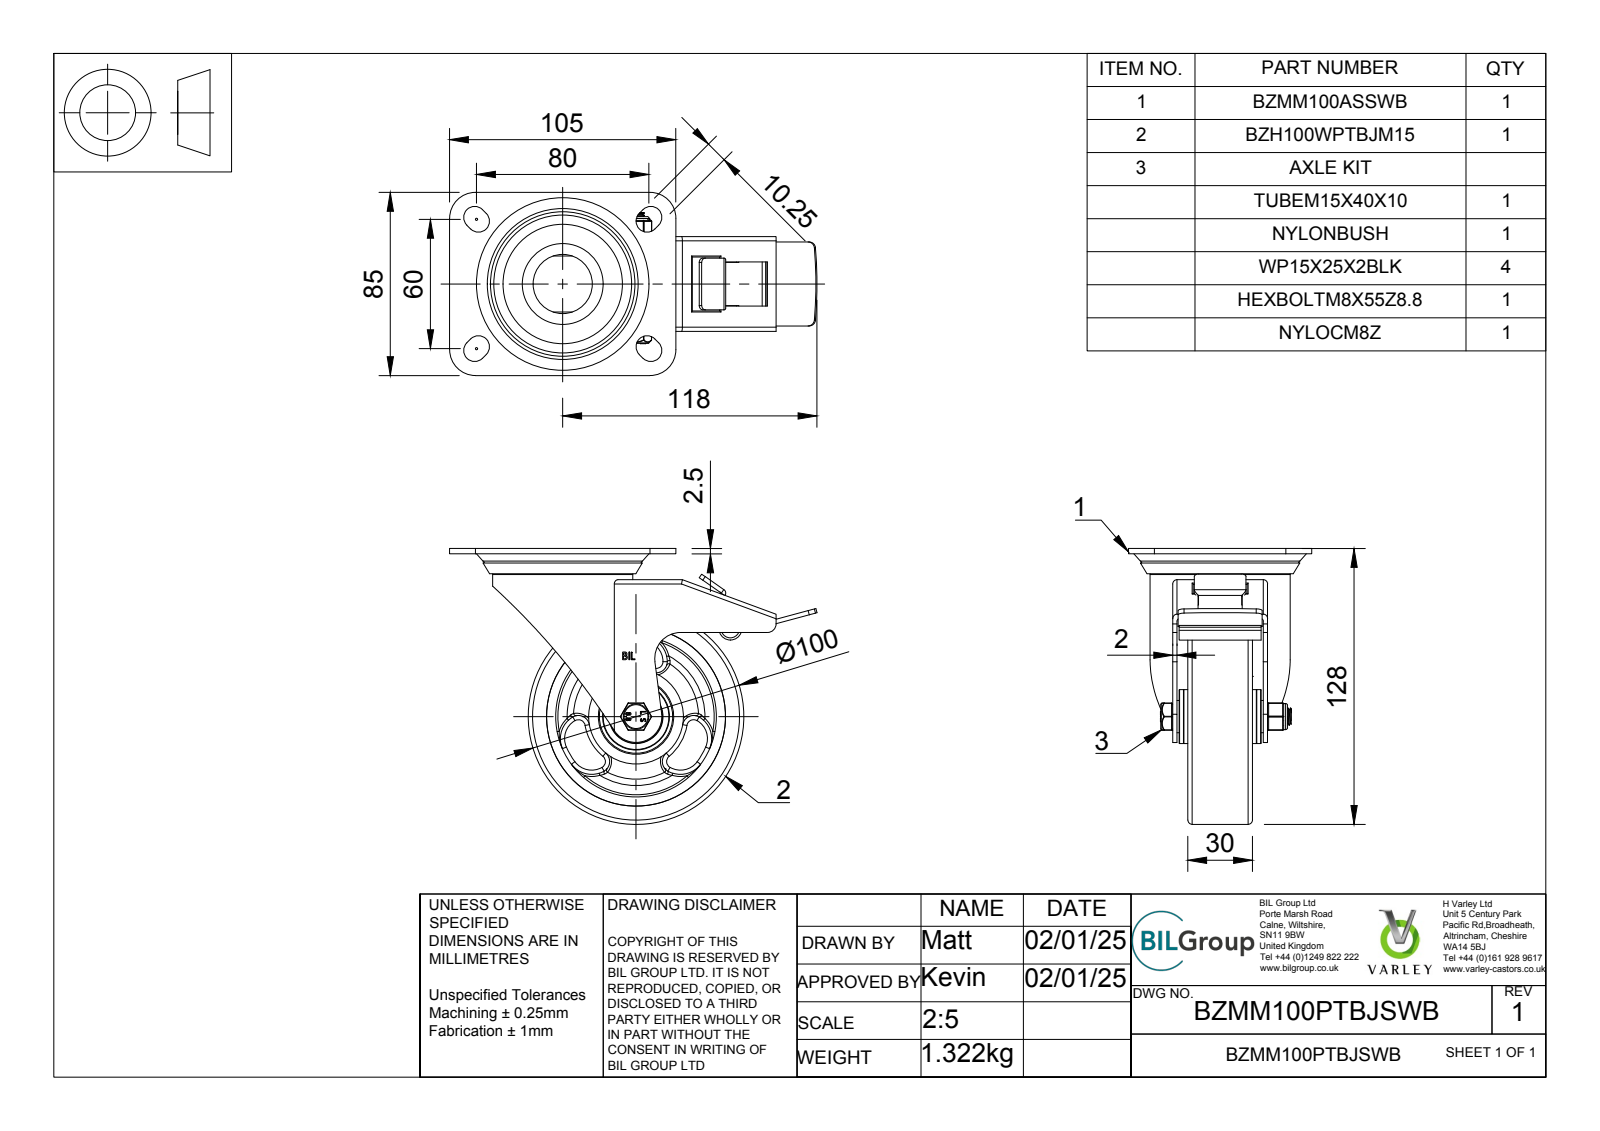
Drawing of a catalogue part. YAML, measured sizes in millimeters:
part_name: "BZMM100PTBJSWB v5; BZMM100ASSWB v1; ZINC PLATED, PRESSED STEEL TOP PLATE; ZINC PLATED, PRESSED STEEL TOP PLATE Geometry (+7 more)"
step_written_by: "Autodesk Translation Framework v13.20.0.188 (AP242_MANAGED_MODEL_BASED_3D_ENGINEERING_MIM_LF)"
units: millimeters
bodies: {solids: 67, faces: 1418, planar: 569, cylindrical: 282, other: 567}
overall_size: [170.5, 128, 85]
volume: 240482
surface_area: 151107
round_holes:
  - {diameter: 0.66, count: 2}
  - {diameter: 8, count: 1}
  - {diameter: 8.2, count: 1}
  - {diameter: 8.6, count: 1}
  - {diameter: 10.2, count: 1}
  - {diameter: 15, count: 1}
  - {diameter: 15.75, count: 1}
  - {diameter: 20, count: 1}
  - {diameter: 22.5, count: 1}
  - {diameter: 27.5, count: 1}
  - {diameter: 30, count: 1}
  - {diameter: 31, count: 1}
round_bosses_or_shafts:
  - {diameter: 100, count: 1}
  - {diameter: 65, count: 1}
  - {diameter: 44, count: 1}
  - {diameter: 31.5, count: 1}
  - {diameter: 30.5, count: 1}
  - {diameter: 25, count: 1}
  - {diameter: 23, count: 1}
  - {diameter: 19, count: 1}
partial_cylinders:
  - {radius: 0.5, count: 22}
  - {radius: 5.12, count: 20}
  - {radius: 0.25, count: 12}
  - {radius: 11.64, count: 12}
  - {radius: 2, count: 9}
  - {radius: 1, count: 6}
  - {radius: 12, count: 6}
  - {radius: 0.33, count: 4}
face_to_face_distances: [2, 37, 5, 1, 35, 7, 42, 30, 2.5, 14.5]
hole_center_spacings: [3.22, 2.49]
